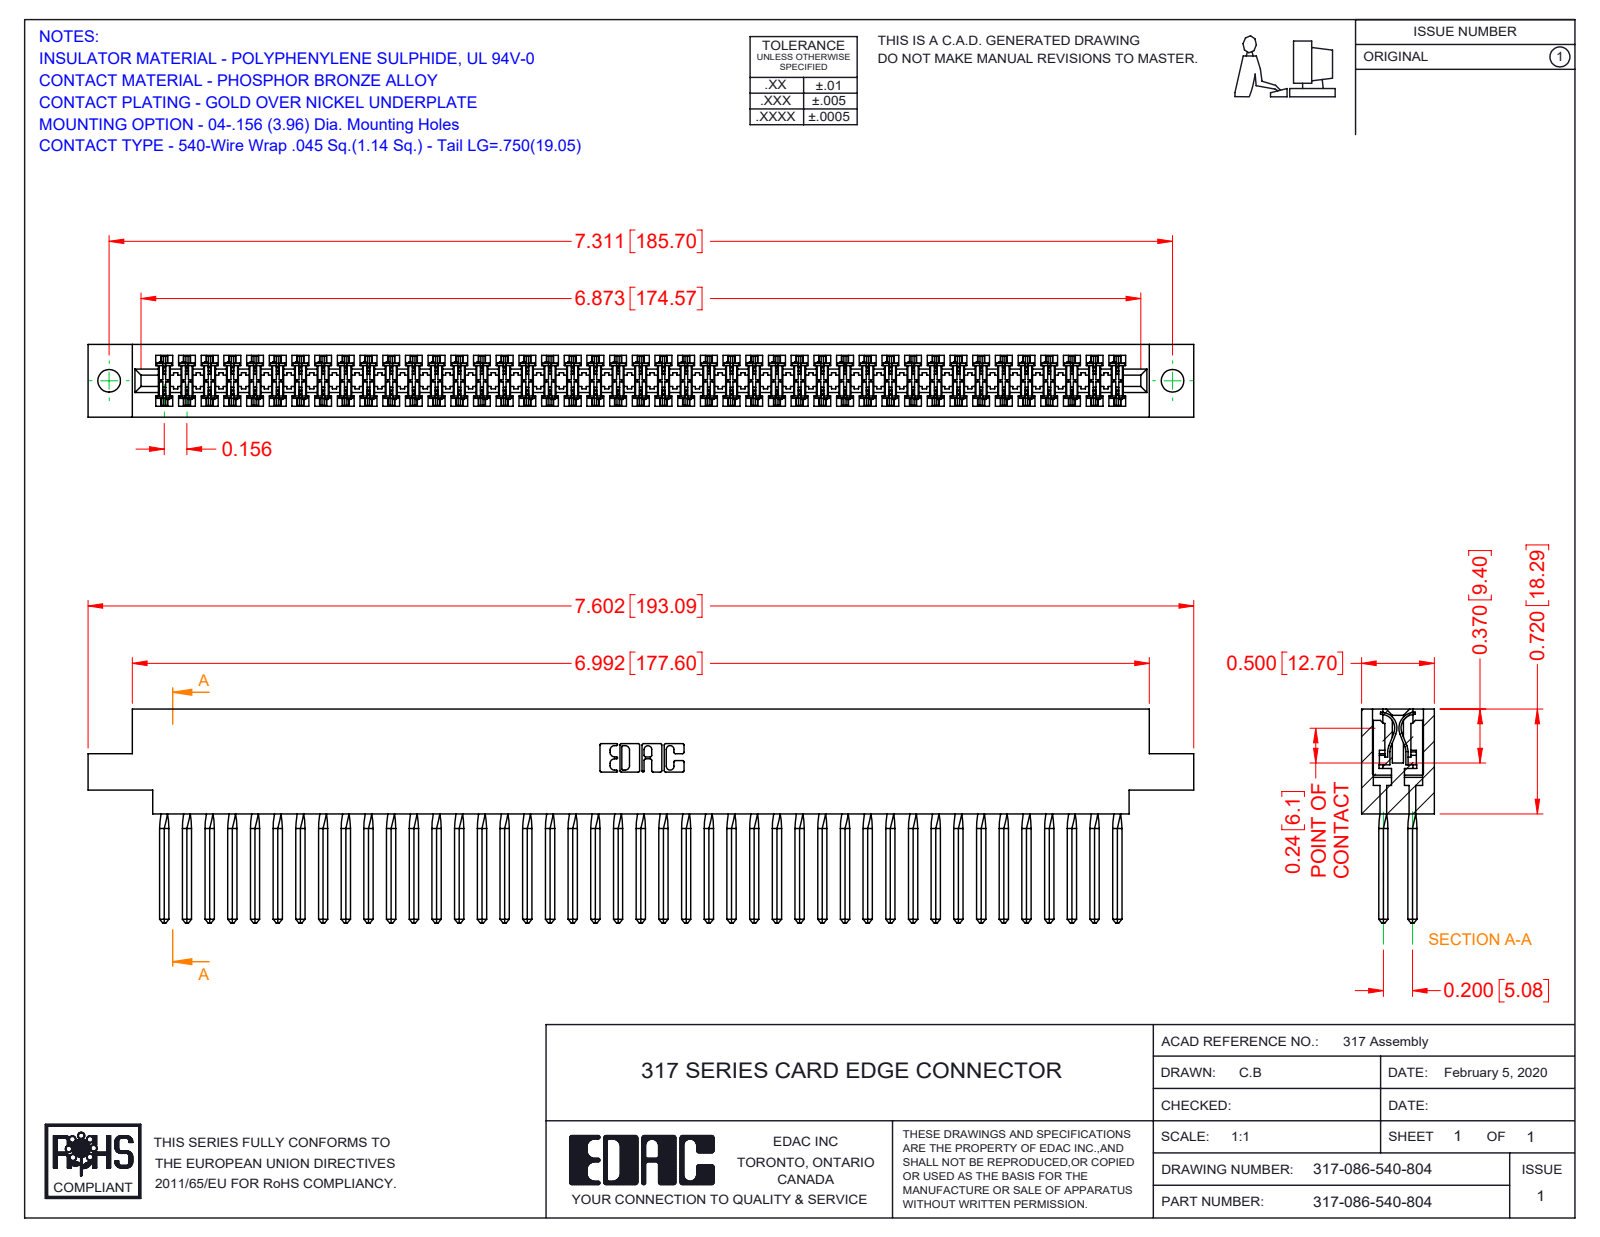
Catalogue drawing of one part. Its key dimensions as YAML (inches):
part_name: "317 Part_.156 Dia - TH; 317-086-540-804; 317-290-001_540"
step_written_by: "SolidWorks 2016 (CONFIG_CONTROL_DESIGN)"
units: inches
bodies: {solids: 87, faces: 7756, planar: 6336, cylindrical: 1076, other: 344}
overall_size: [7.602, 1.47, 0.5]
volume: 1.974
surface_area: 74.55
round_holes:
  - {diameter: 0.156, count: 2}
partial_cylinders:
  - {radius: 0.015, count: 172}
  - {radius: 0.01, count: 22}
  - {radius: 0.007, count: 6}
  - {radius: 0.031, count: 6}
  - {radius: 0.026, count: 3}
  - {radius: 0.095, count: 2}
  - {radius: 0.1, count: 2}
  - {radius: 0.11, count: 2}
face_to_face_distances: [0.5, 0.075, 0.425, 0.35, 0.195, 0.094, 0.2, 0.115, 0.131, 0.046]
hole_center_spacings: [7.311]
